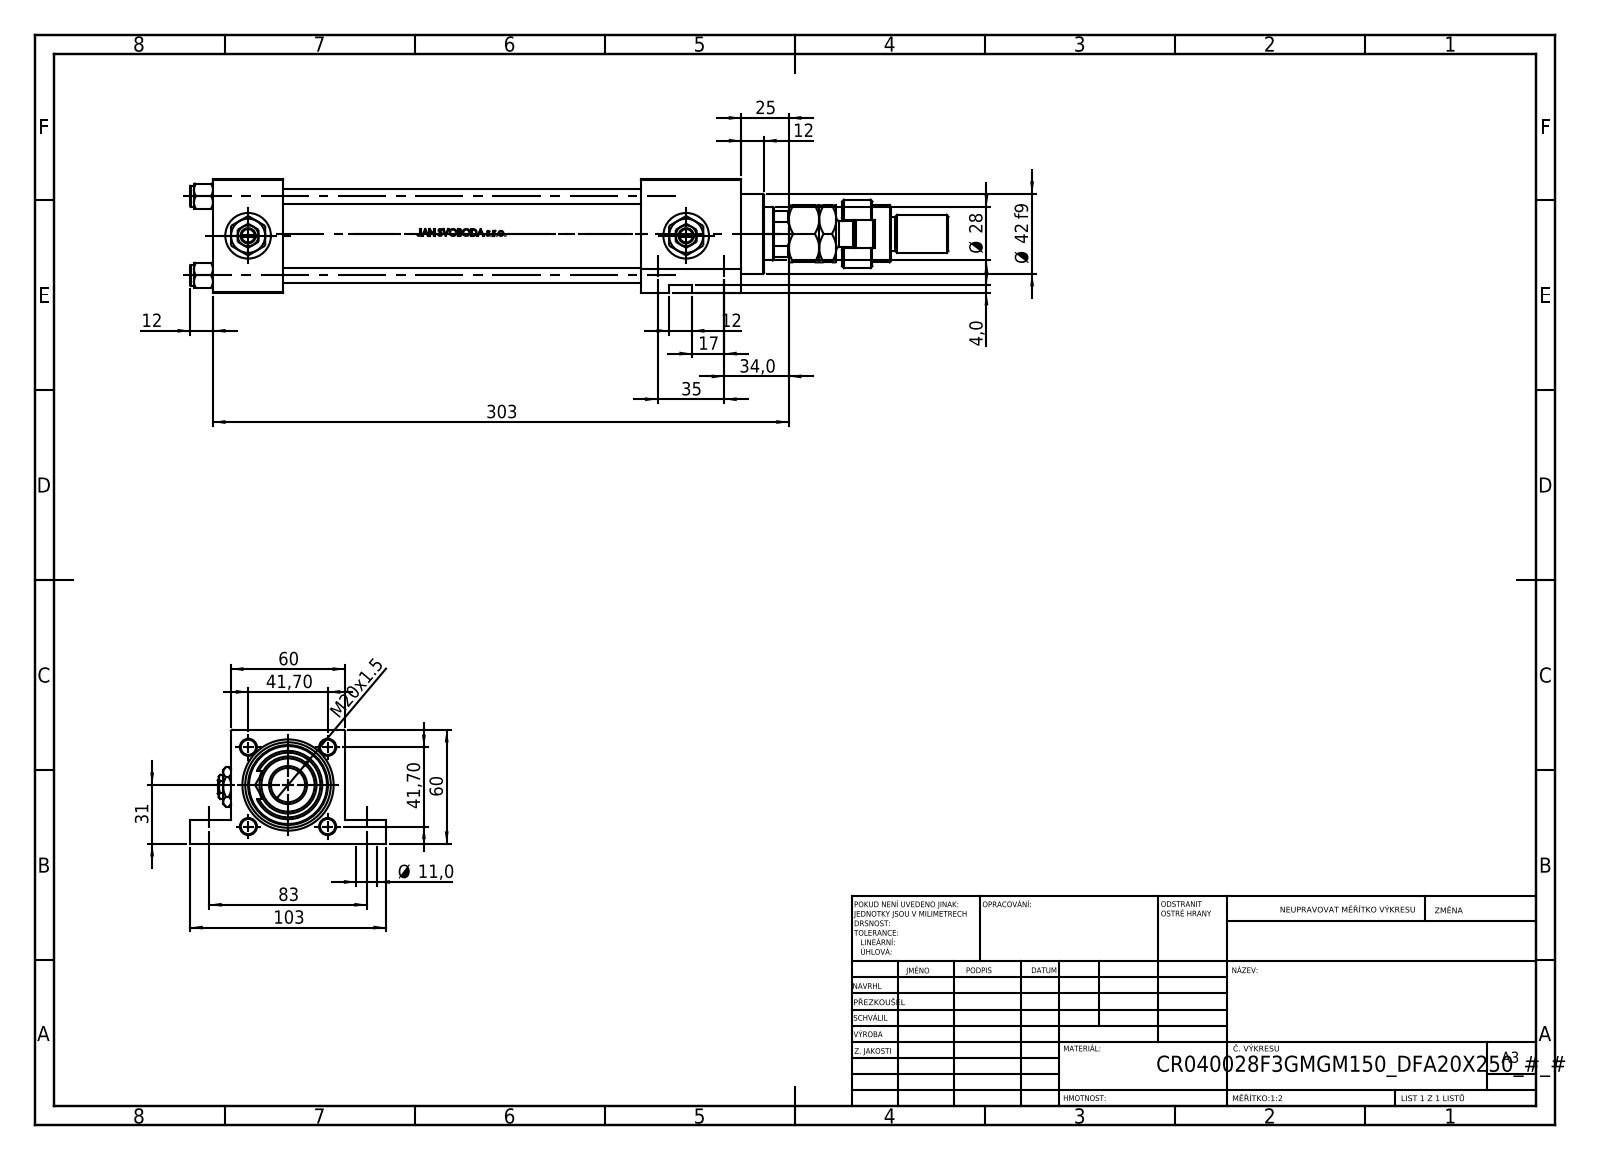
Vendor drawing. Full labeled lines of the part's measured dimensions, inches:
Part name (STEP PRODUCT): NUT_M5_F; V215CR_F_Body; Zatka_pro_OIL_PORT; V215CR_F_TYCINKA (+4 more)
STEP written by: SolidWorks 2019 (CONFIG_CONTROL_DESIGN)
Units: inches
Bodies: 15 solids, 1300 faces (512 planar, 162 cylindrical, 626 other)
Overall size (bounding box): 15.709 × 4.055 × 2.362
Volume: 39.64 in³ · Surface area: 299.9 in²
Round holes (diameter × count): ⌀0.315 ×4, ⌀0.433 ×4, ⌀0.656 ×3, ⌀0.945 ×3, ⌀0.276 ×2, ⌀0.63 ×1, ⌀0.728 ×1, ⌀1.102 ×1, ⌀1.22 ×1, ⌀1.575 ×1, ⌀1.772 ×1
Round bosses / shafts (diameter × count): ⌀0.433 ×4, ⌀1.811 ×1, ⌀1.654 ×1, ⌀1.417 ×1, ⌀1.181 ×1, ⌀0.866 ×1, ⌀0.787 ×1, ⌀0.709 ×1
Partial cylindrical surfaces — rounded edges, fillets, slot ends (radius × count): R0.295 ×1, R0.472 ×1, R0.531 ×1
Main face-to-face distances: 2.362, 1.457, 2.087, 8.858, 7.402, 10.945, 1.496, 9.488, 0.492, 1.87
Hole centre spacings: 1.642, 1.133, 1.189, 1.378, 2.322, 3.268, 3.546, 0.315
